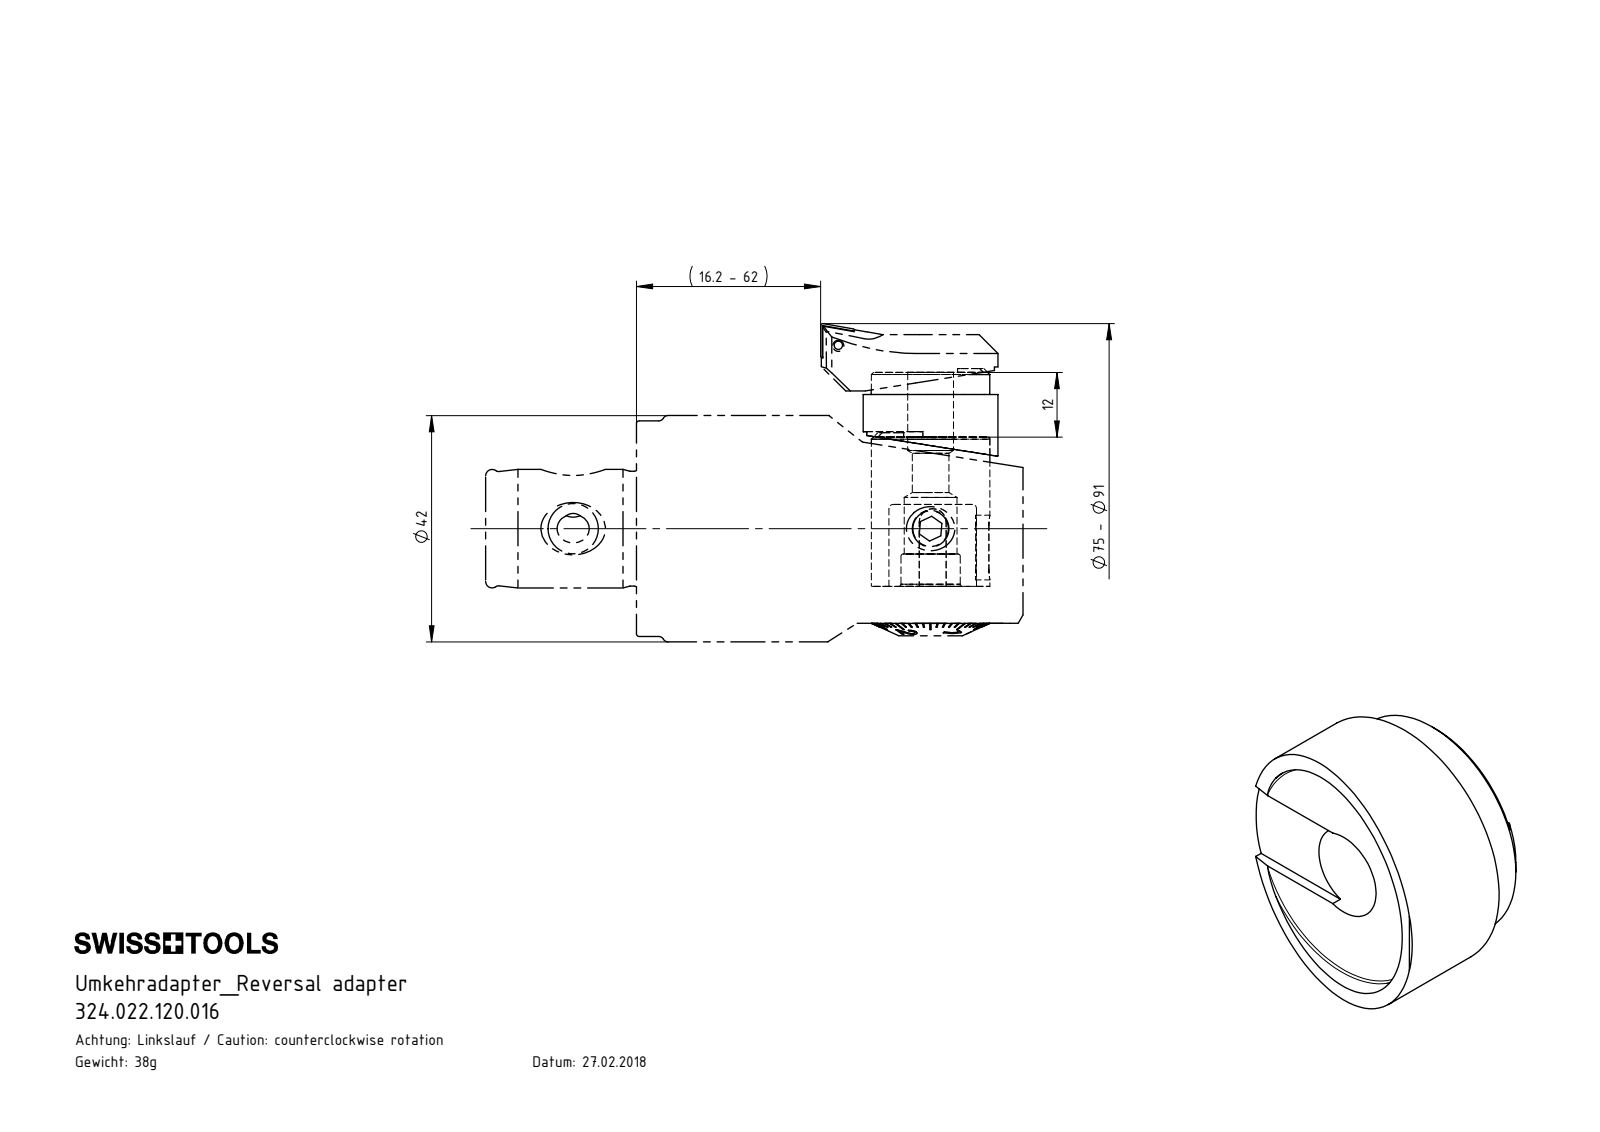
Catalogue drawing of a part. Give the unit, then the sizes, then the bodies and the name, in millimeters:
Units: millimetres
Overall size (bounding box): 25 × 25 × 16.2
Round holes (diameter × count): ⌀8.5 ×1, ⌀22 ×1
Round bosses / shafts (diameter × count): ⌀25 ×1
Partial cylindrical surfaces — rounded edges, fillets, slot ends (radius × count): R0.5 ×2
Main face-to-face distances: 12, 4.1, 7.9, 11, 6.9, 1, 0.7, 4.8, 11.7, 12.7
Volume: 4 886 mm³ · Surface area: 2 325 mm²
Bodies: 1 solid, 28 faces (12 planar, 11 cylindrical, 5 other)
Part name (STEP PRODUCT): F42-U00.001.012_B; 324.022.120.016
STEP written by: SolidWorks 2017 (CONFIG_CONTROL_DESIGN)
